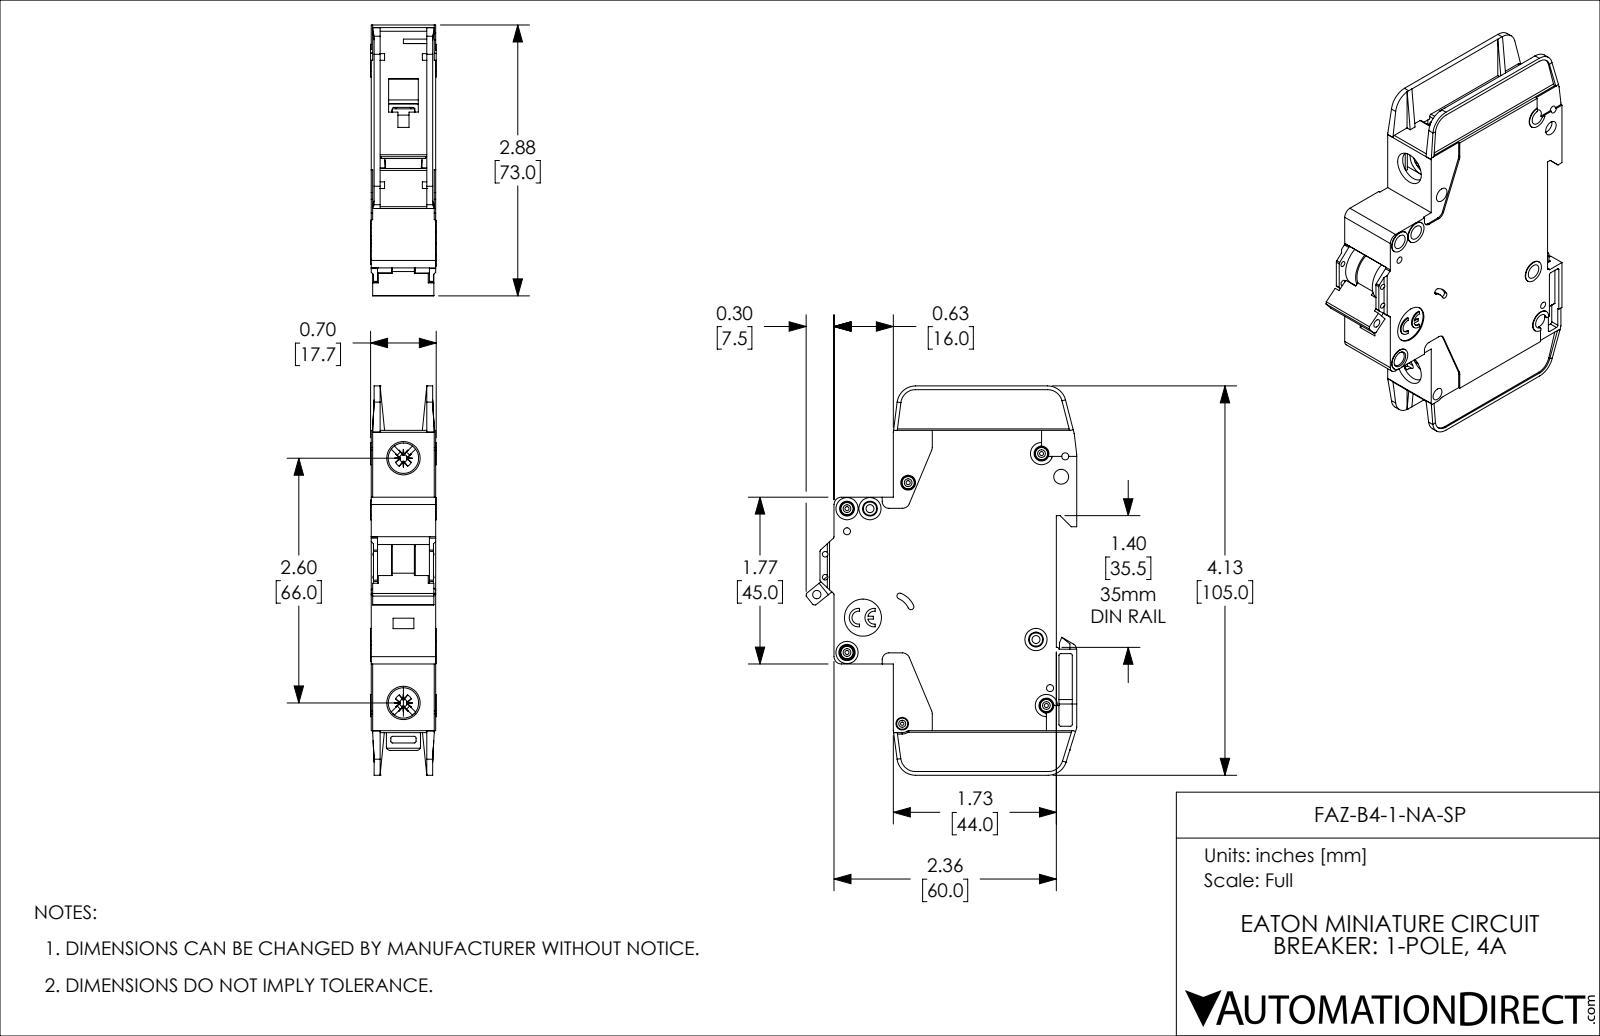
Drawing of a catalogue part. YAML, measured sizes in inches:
part_name: "FAZ-B4-1-NA-SP"
step_written_by: "SolidWorks 2019 (AUTOMOTIVE_DESIGN)"
units: inches
bodies: {solids: 1, faces: 1127, planar: 671, cylindrical: 357, other: 99}
overall_size: [4.134, 2.876, 0.697]
volume: 4.682
surface_area: 41.01
round_holes:
  - {diameter: 0.157, count: 8}
  - {diameter: 0.043, count: 5}
  - {diameter: 0.075, count: 4}
  - {diameter: 0.059, count: 2}
  - {diameter: 0.085, count: 2}
  - {diameter: 0.323, count: 2}
  - {diameter: 0.035, count: 1}
  - {diameter: 0.089, count: 1}
  - {diameter: 0.098, count: 1}
  - {diameter: 0.134, count: 1}
  - {diameter: 0.394, count: 1}
round_bosses_or_shafts:
  - {diameter: 0.13, count: 5}
  - {diameter: 0.236, count: 4}
  - {diameter: 0.118, count: 2}
  - {diameter: 0.098, count: 1}
partial_cylinders:
  - {radius: 0.02, count: 42}
  - {radius: 0.016, count: 10}
  - {radius: 0.039, count: 10}
  - {radius: 0.079, count: 8}
  - {radius: 0.197, count: 5}
  - {radius: 0.008, count: 4}
  - {radius: 0.026, count: 4}
  - {radius: 0.043, count: 4}
face_to_face_distances: [0.047, 0.685, 0.591, 0.638, 0.094, 0.543, 0.016, 0.031, 0.496, 0.575]
hole_center_spacings: [0.244, 0.537, 0.87, 0.189, 0.199, 0.204, 0.221, 0.24]
